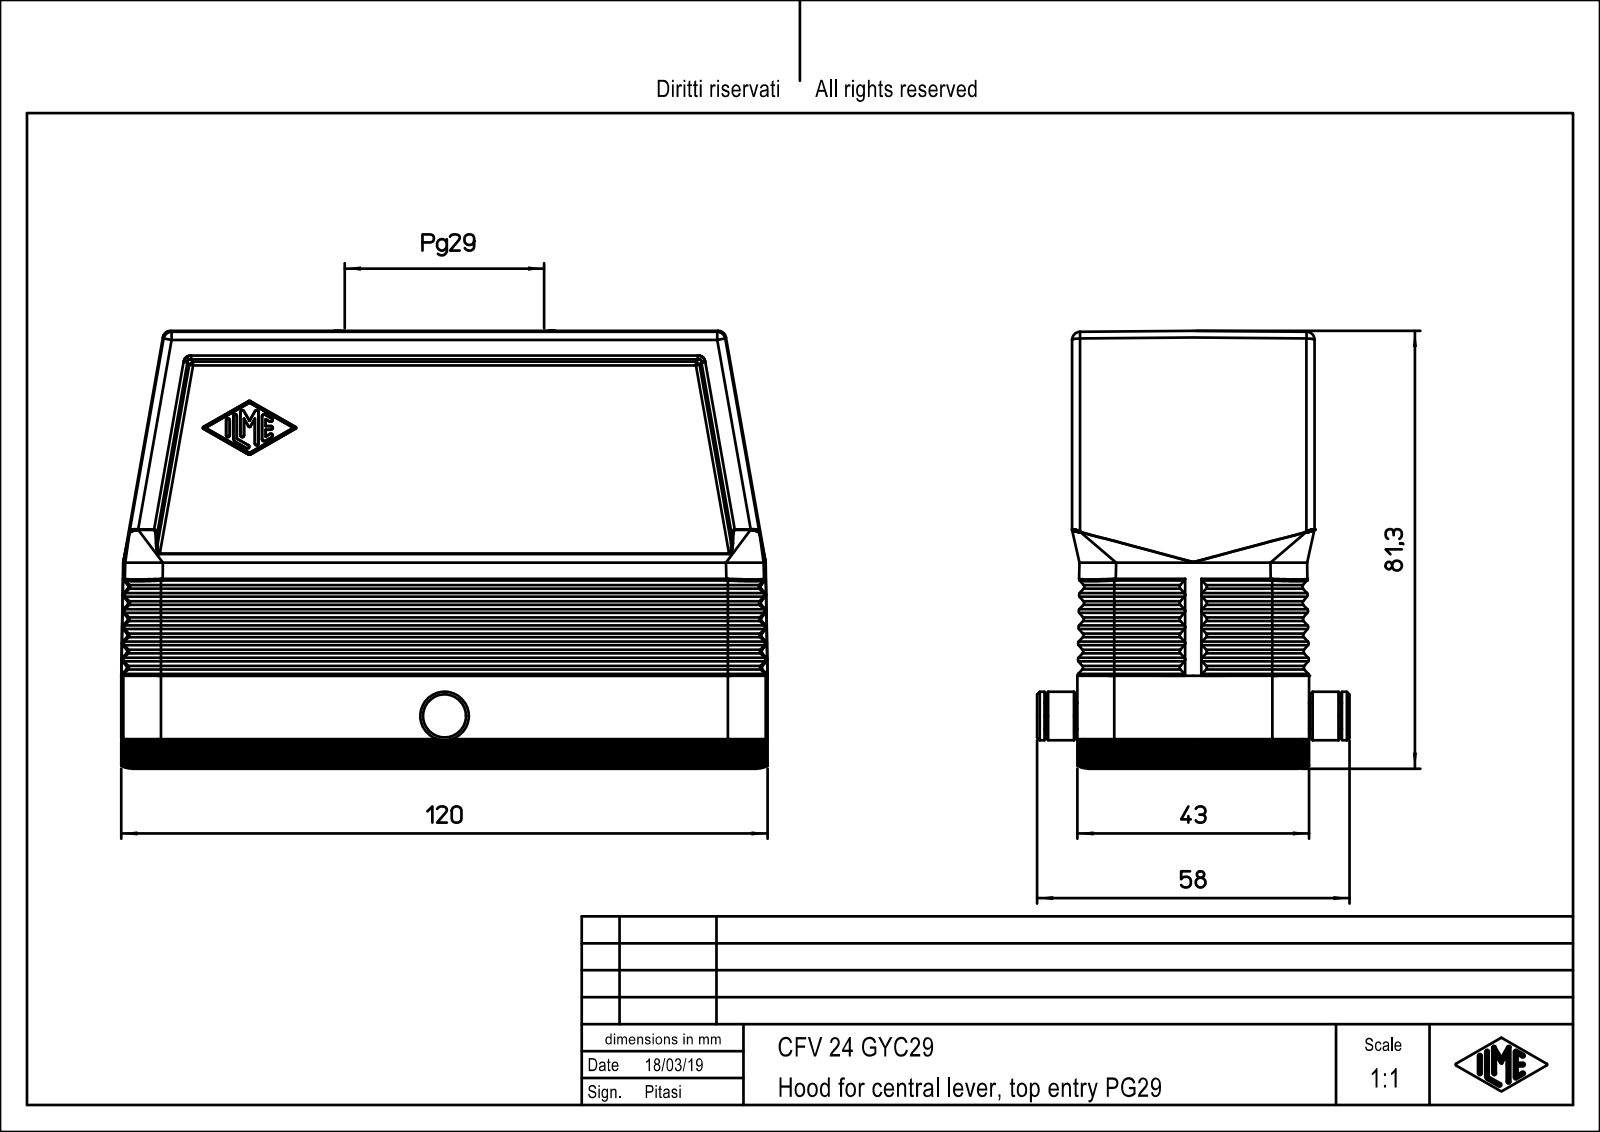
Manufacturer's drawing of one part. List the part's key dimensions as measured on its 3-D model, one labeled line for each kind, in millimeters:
Part name (STEP PRODUCT): CFV_24_GYC29
STEP written by: PTC Creo Elements/Direct Modeling 19.0E 27-Jun-2016 (C) Parametric Technology GmbH (AUTOMOTIVE_DESIGN)
Units: millimetres
Bodies: 1 solid, 576 faces (226 planar, 182 cylindrical, 168 other)
Overall size (bounding box): 120 × 81.25 × 58
Volume: 122 355 mm³ · Surface area: 58 150 mm²
Round holes (diameter × count): ⌀3 ×4, ⌀36.24 ×1
Round bosses / shafts (diameter × count): ⌀9 ×1, ⌀4.8 ×1
Partial cylindrical surfaces — rounded edges, fillets, slot ends (radius × count): R0.5 ×84, R1 ×16, R7 ×12, R1.5 ×10, R3 ×8, R3.5 ×4, R4 ×4, R4.2 ×4
Main face-to-face distances: 43, 1.01, 4, 2, 6, 39, 44, 1, 5, 40
Hole centre spacings: 27, 53.71, 53.72, 103.99, 107.44
